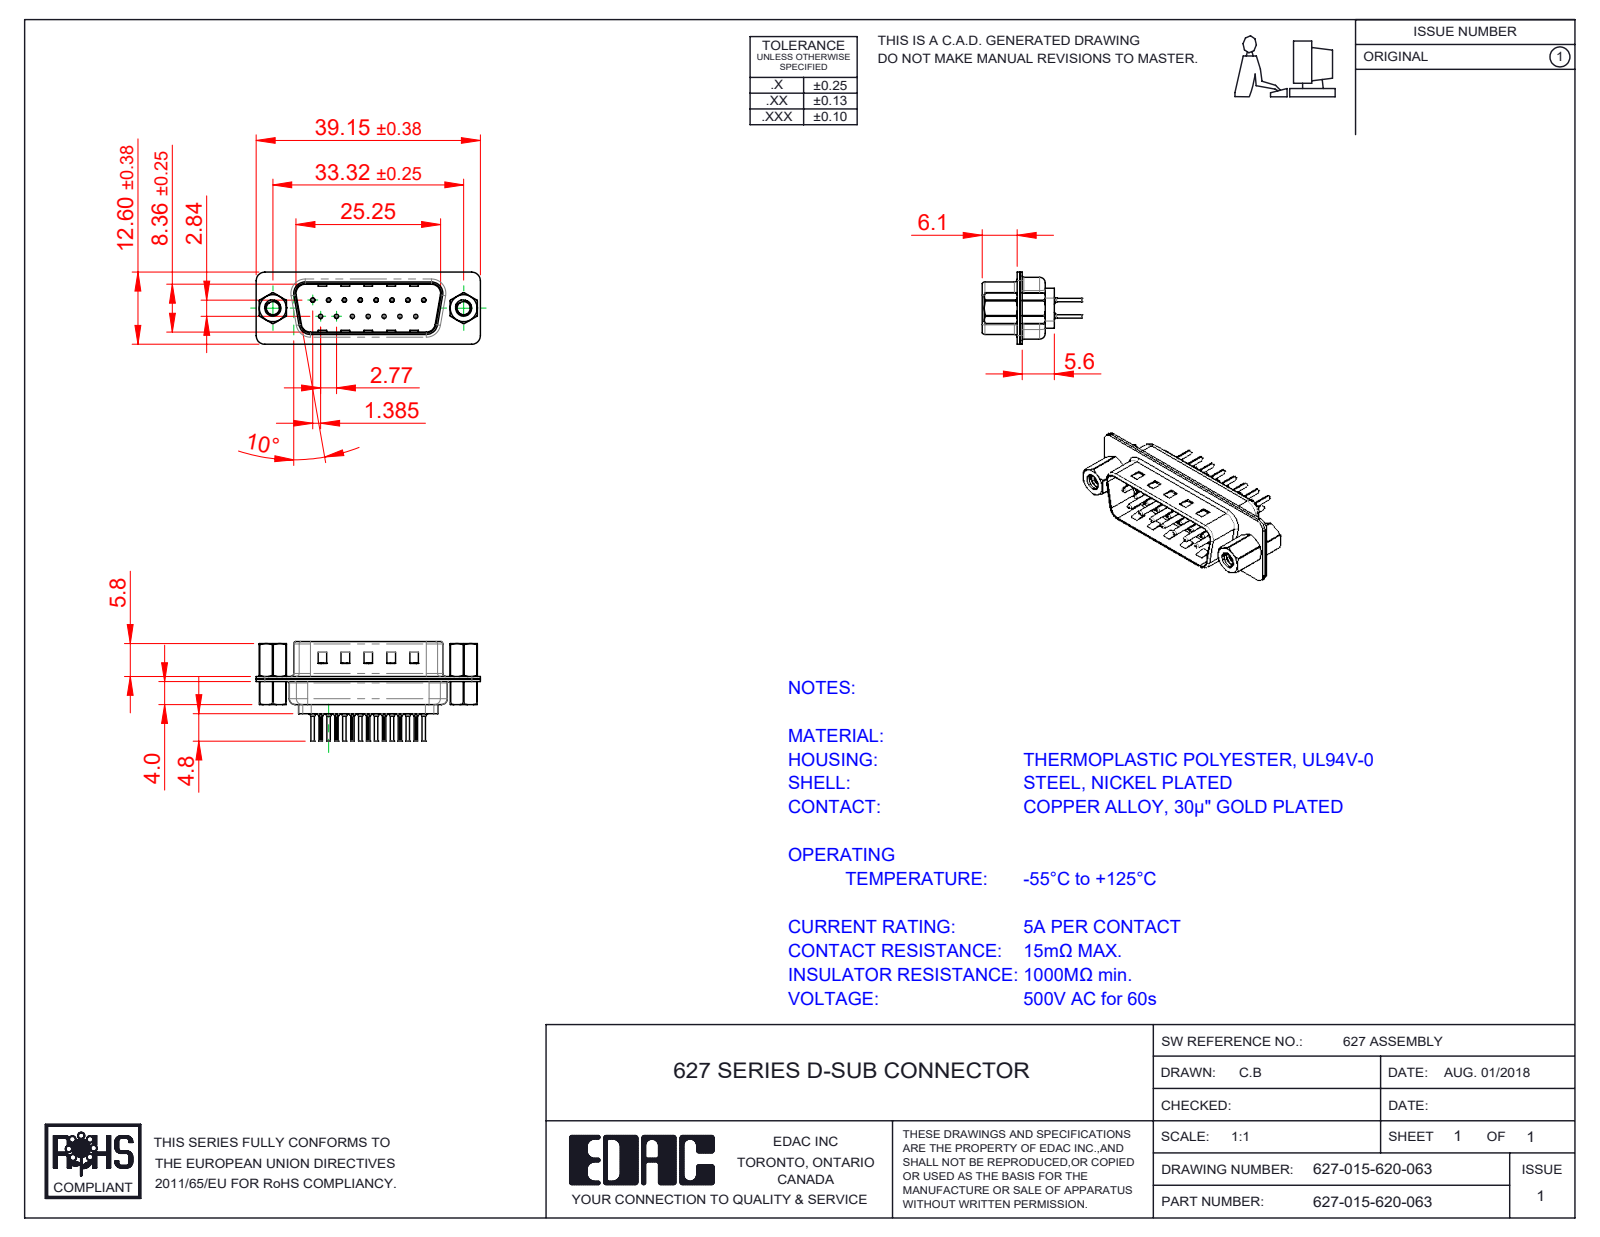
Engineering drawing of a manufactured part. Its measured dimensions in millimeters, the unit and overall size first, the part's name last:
Units: millimetres
Overall size (bounding box): 39.15 × 17.3 × 12.6
Round holes (diameter × count): ⌀0.2 ×15, ⌀0.35 ×15, ⌀1.1 ×15, ⌀1.6 ×15, ⌀2.26 ×2, ⌀2.29 ×2, ⌀4 ×2, ⌀4.8 ×2
Round bosses / shafts (diameter × count): ⌀2 ×15, ⌀1.5 ×15, ⌀0.75 ×15, ⌀0.6 ×15, ⌀5 ×2, ⌀4.9 ×2, ⌀2.79 ×2
Partial cylindrical surfaces — rounded edges, fillets, slot ends (radius × count): R0.1 ×30, R1.5 ×16, R2 ×12, R0.5 ×8, R1.6 ×8, R0.25 ×4, R0.6 ×4, R0.65 ×4
Main face-to-face distances: 0.4, 0.45, 0.9, 0.82, 9.58, 8.76, 1.5, 1.4, 6.5, 5.6
Hole centre spacings: 3.16, 2.77, 5.54, 8.31, 11.08, 5.03, 5.04, 7.48
Volume: 2 038 mm³ · Surface area: 5 864 mm²
Bodies: 22 solids, 1932 faces (521 planar, 758 cylindrical, 653 other)
Part name (STEP PRODUCT): 627 Shell Rear_15 Contacts; 627 Shell Front_15 Contacts; 627 Contact Row 2_20L; 627-015-620-063 (+4 more)
STEP written by: SolidWorks 2020 (CONFIG_CONTROL_DESIGN)
